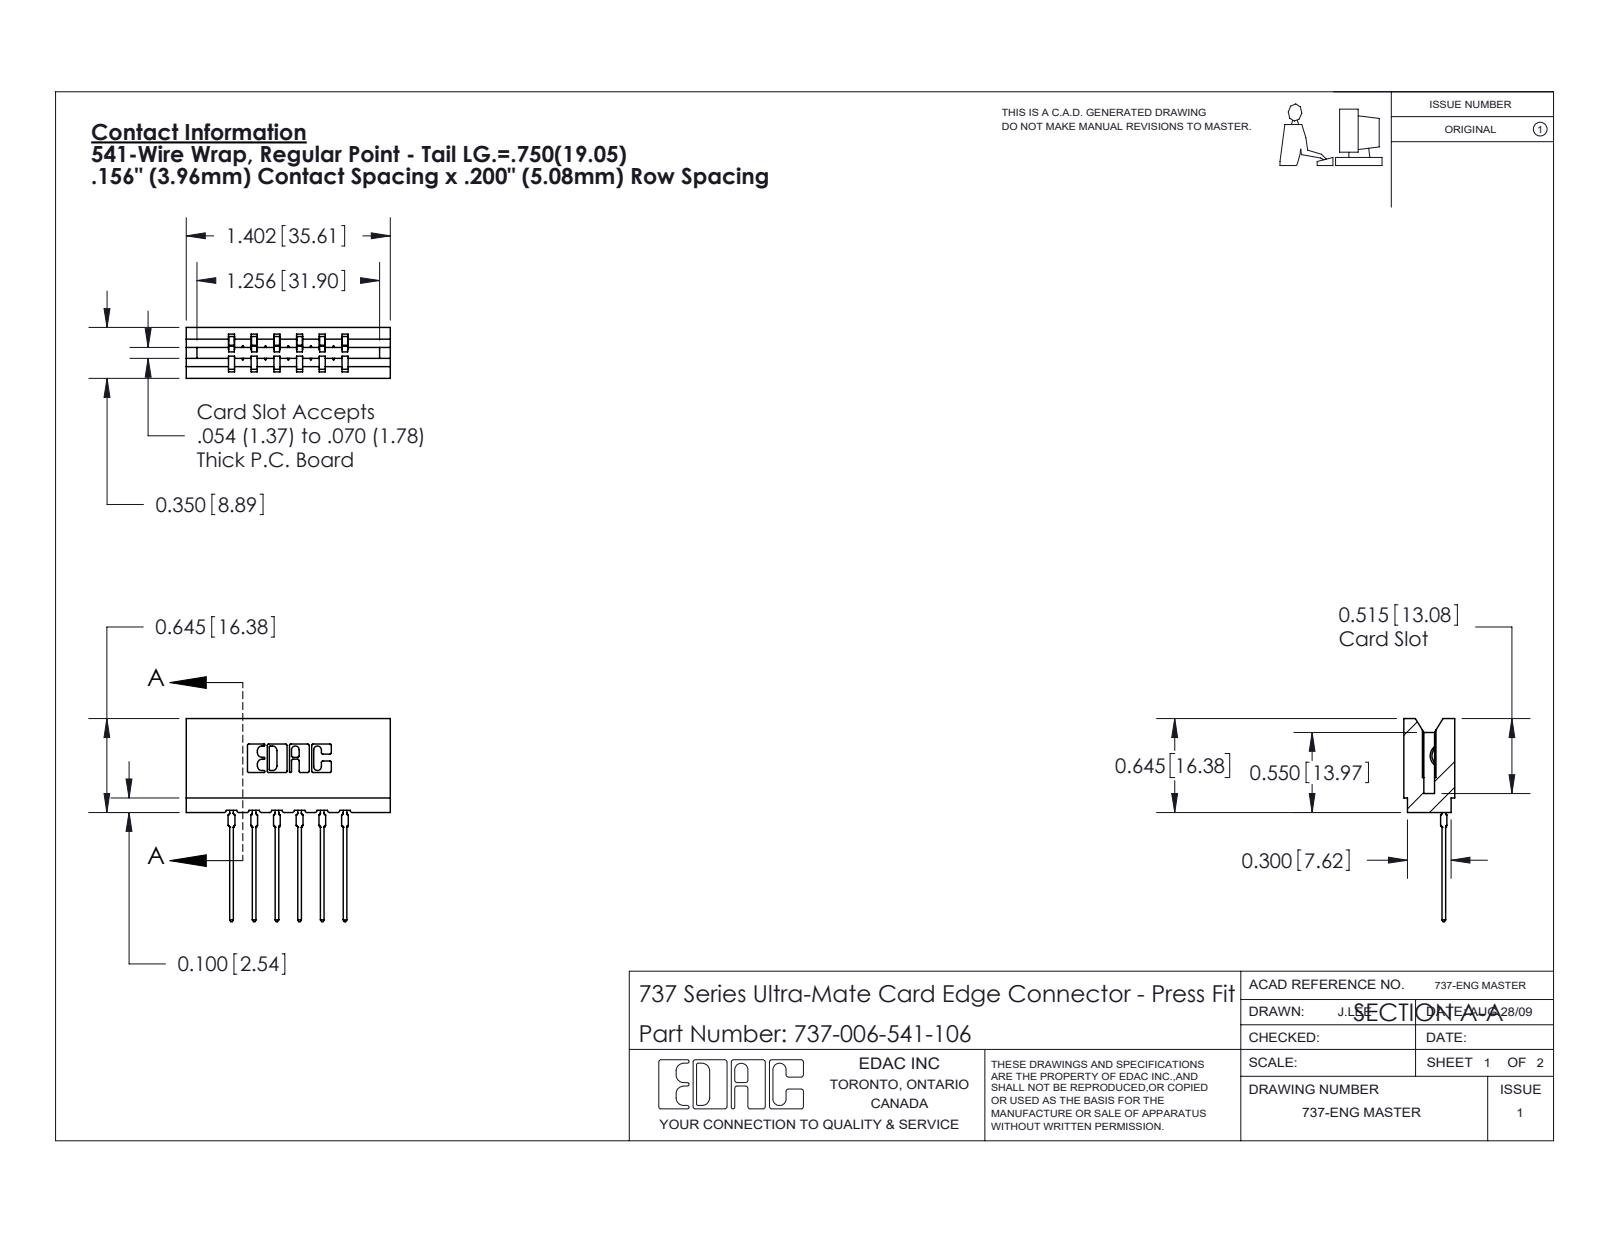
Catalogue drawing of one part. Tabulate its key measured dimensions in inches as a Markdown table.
| quantity | value |
| --- | --- |
| part name | 745-292-001_541; 737-006-541-106; 737 Part_Insulator Option - 06 |
| STEP written by | SolidWorks 2020 (CONFIG_CONTROL_DESIGN) |
| units | inches |
| bodies | 7 solids, 773 faces (463 planar, 154 cylindrical, 156 other) |
| overall size | 1.402 × 1.396 × 0.35 |
| volume | 0.226 in³ |
| surface area | 6.882 in² |
| partial cylindrical surfaces (radius × count) | 0.01 × 22, 0.015 × 12, 0.021 × 12, 0.007 × 6, 0.031 × 6, 0.005 × 4, 0.011 × 4, 0.026 × 3 |
| main face-to-face distances | 0.156, 0.138, 0.212, 0.35, 0.312, 0.354, 0.198, 0.074, 0.468, 0.51 |
